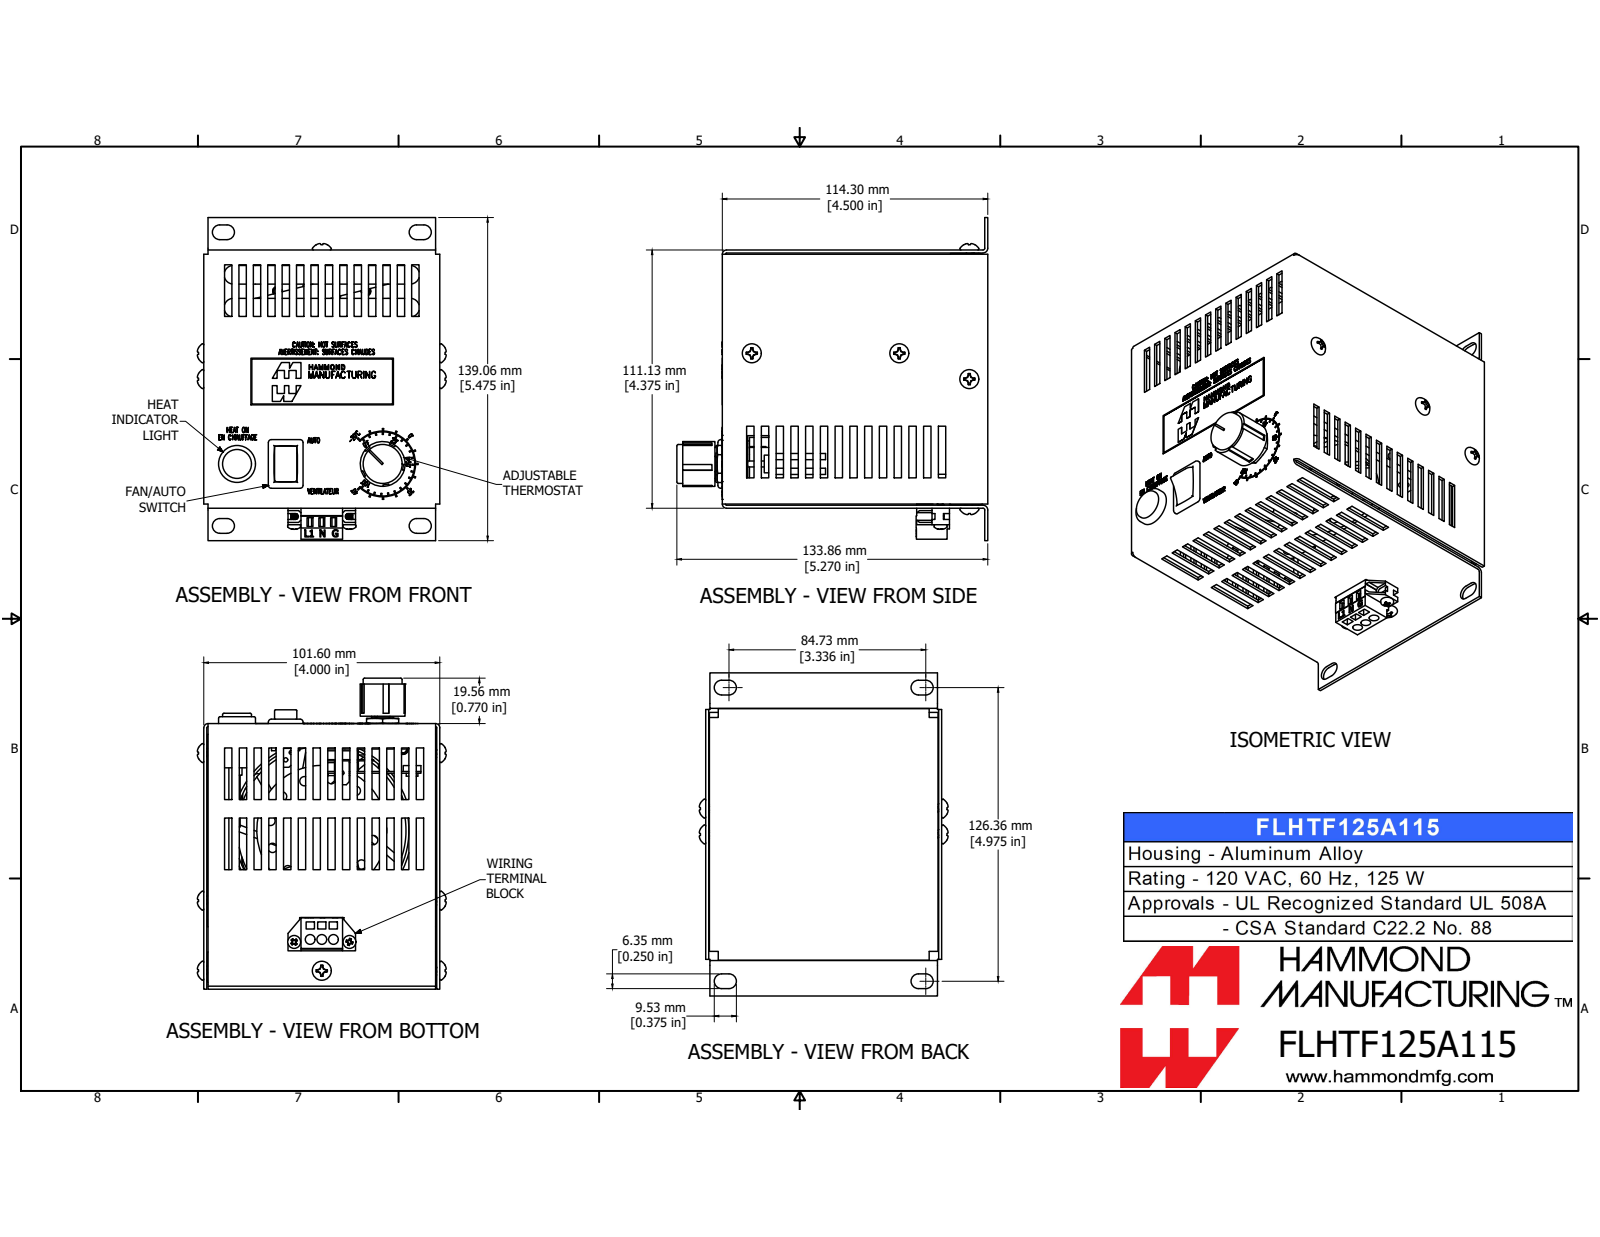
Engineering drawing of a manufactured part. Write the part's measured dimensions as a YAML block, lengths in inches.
part_name: "FLHTF125A115"
step_written_by: "SolidWorks 2019 (AUTOMOTIVE_DESIGN)"
units: inches
bodies: {solids: 17, faces: 4140, planar: 3640, cylindrical: 274, other: 226}
overall_size: [5.475, 5.27, 4.218]
volume: 8.774
surface_area: 274
round_holes:
  - {diameter: 0.137, count: 4}
  - {diameter: 0.182, count: 4}
  - {diameter: 0.203, count: 4}
  - {diameter: 0.165, count: 3}
  - {diameter: 0.085, count: 2}
  - {diameter: 0.12, count: 2}
  - {diameter: 0.13, count: 2}
  - {diameter: 0.189, count: 2}
  - {diameter: 0.066, count: 1}
  - {diameter: 0.07, count: 1}
  - {diameter: 0.25, count: 1}
  - {diameter: 0.383, count: 1}
round_bosses_or_shafts:
  - {diameter: 0.164, count: 4}
  - {diameter: 0.104, count: 4}
  - {diameter: 0.17, count: 2}
  - {diameter: 0.105, count: 2}
  - {diameter: 0.76, count: 1}
  - {diameter: 0.66, count: 1}
  - {diameter: 0.65, count: 1}
  - {diameter: 0.625, count: 1}
partial_cylinders:
  - {radius: 0.125, count: 38}
  - {radius: 0.05, count: 17}
  - {radius: 0.025, count: 12}
  - {radius: 0.629, count: 12}
  - {radius: 0.15, count: 9}
  - {radius: 0.02, count: 4}
  - {radius: 0.071, count: 4}
  - {radius: 0.015, count: 2}
face_to_face_distances: [0.051, 3.949, 0.1, 0.051, 4.324, 4, 3.898, 4.494, 4.394, 4.443]
hole_center_spacings: [2.756, 0.197, 0.275, 0.471, 0.531, 0.564, 0.565, 0.667]
